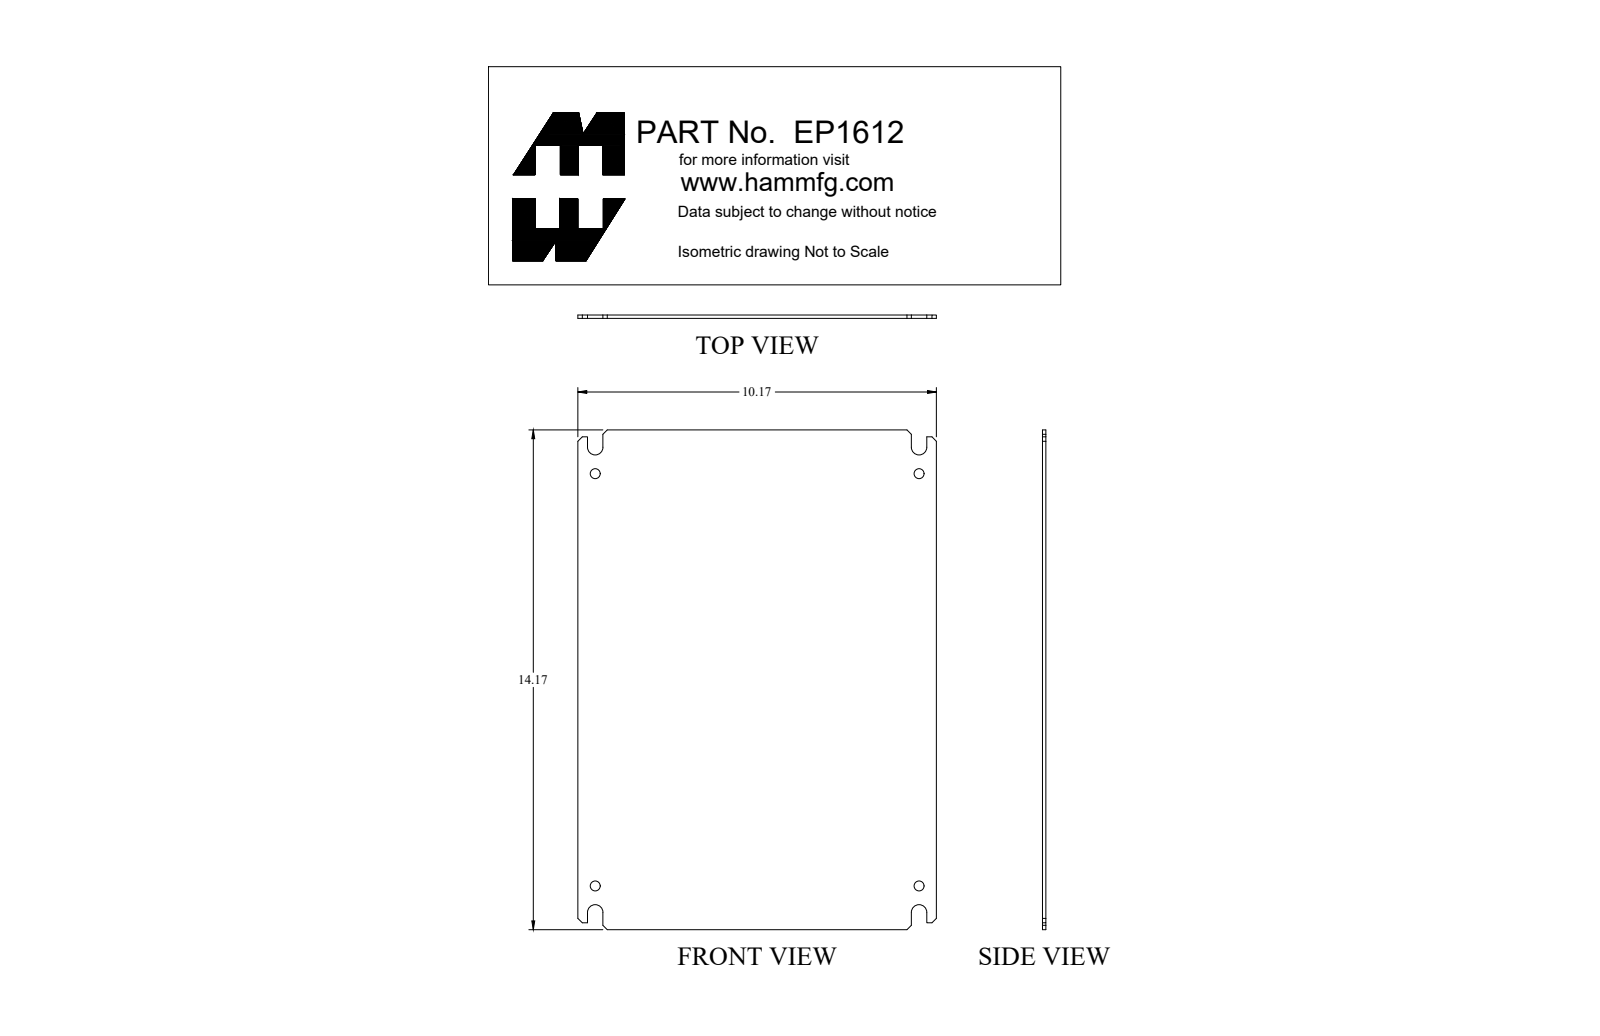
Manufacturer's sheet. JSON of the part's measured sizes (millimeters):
{"part_name": "EP1612", "step_written_by": "SolidWorks 2018 (AUTOMOTIVE_DESIGN)", "units": "millimeters", "bodies": {"solids": 1, "faces": 40, "planar": 26, "cylindrical": 14, "other": 0}, "overall_size": [359.9, 258.3, 2.4], "volume_mm3": 221700, "surface_area_mm2": 187200, "round_holes": [[7.1, 4]], "partial_cylinders_radius": [[5.6, 4]], "face_to_face_distances": [2.4, 258.3, 359.9, 18, 240.3, 6.9, 251.4, 11.1, 233.4, 222.3], "hole_center_spacings": [233.4, 296.9, 377.6]}
